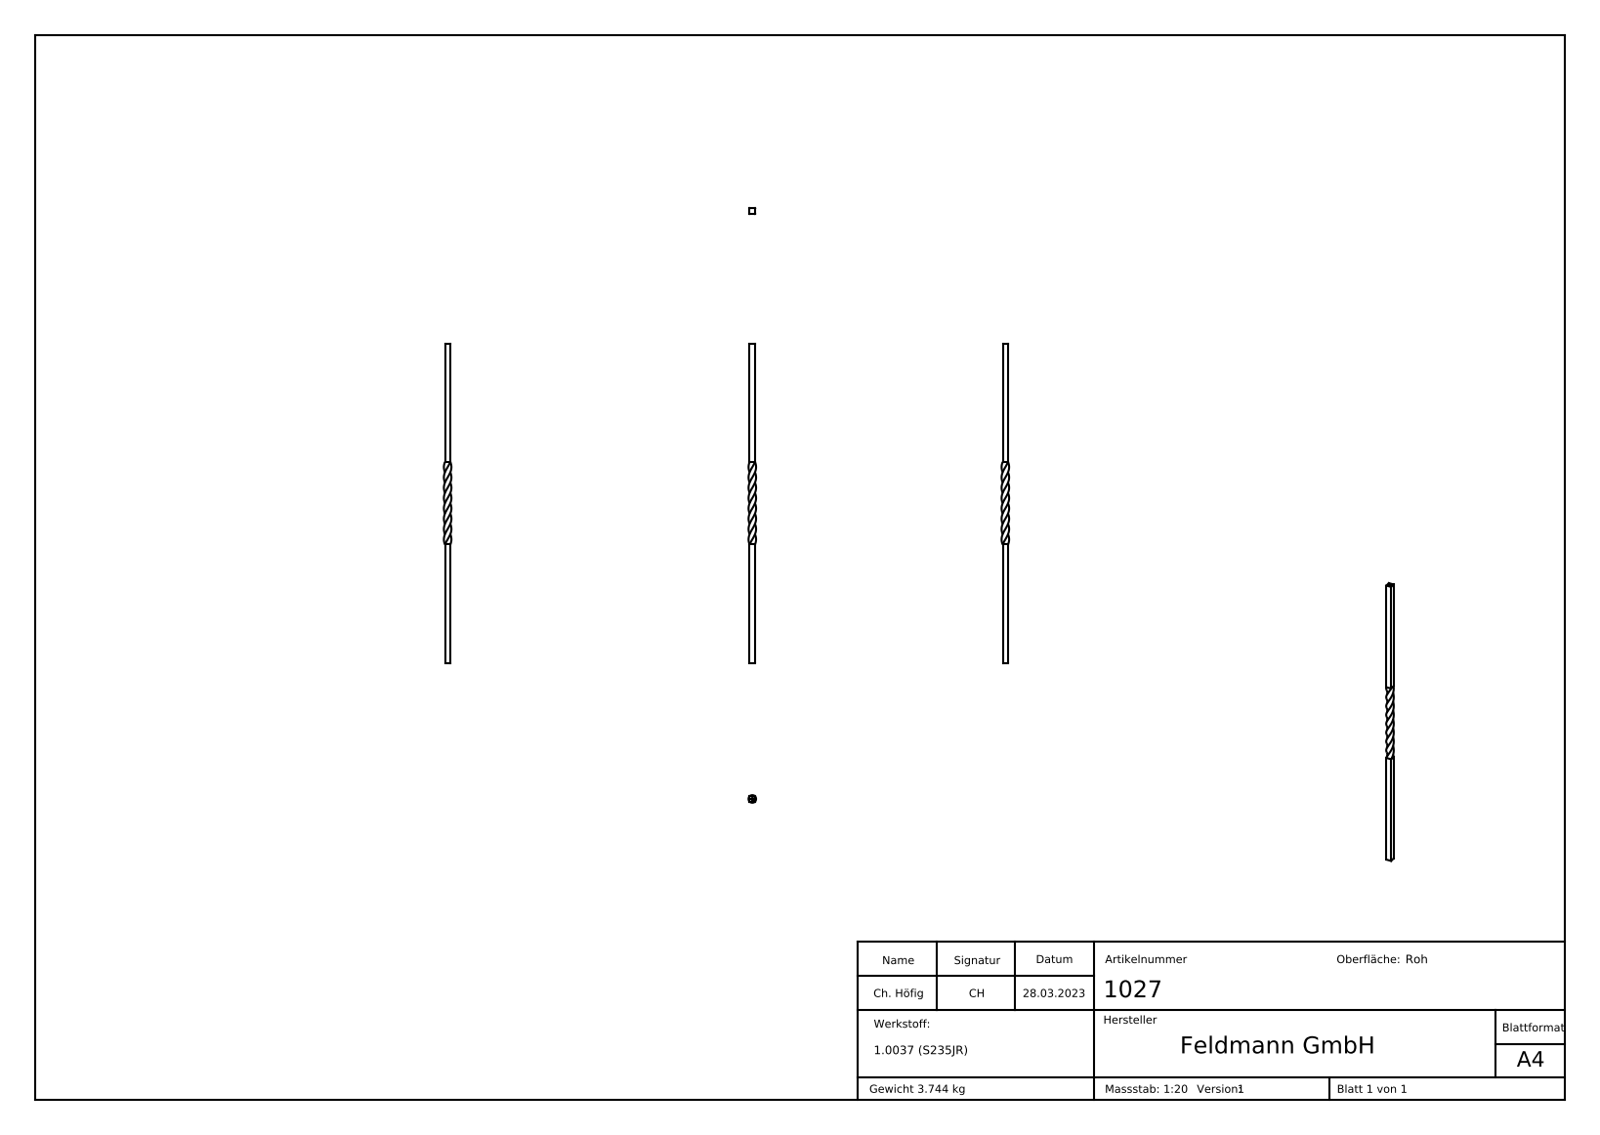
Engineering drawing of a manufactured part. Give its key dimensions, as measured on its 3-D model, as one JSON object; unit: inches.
{"part_name": "1027", "step_written_by": "SolidWorks 2018 (CONFIG_CONTROL_DESIGN)", "units": "inches", "bodies": {"solids": 1, "faces": 165, "planar": 98, "cylindrical": 0, "other": 67}, "overall_size": [47.244, 1.115, 1.115], "volume_in3": 29.29, "surface_area_in2": 151.1, "face_to_face_distances": [0.787, 47.244, 47.24, 0.144, 0.022, 0.106, 0.117, 0.052, 0.394, 0.015]}
